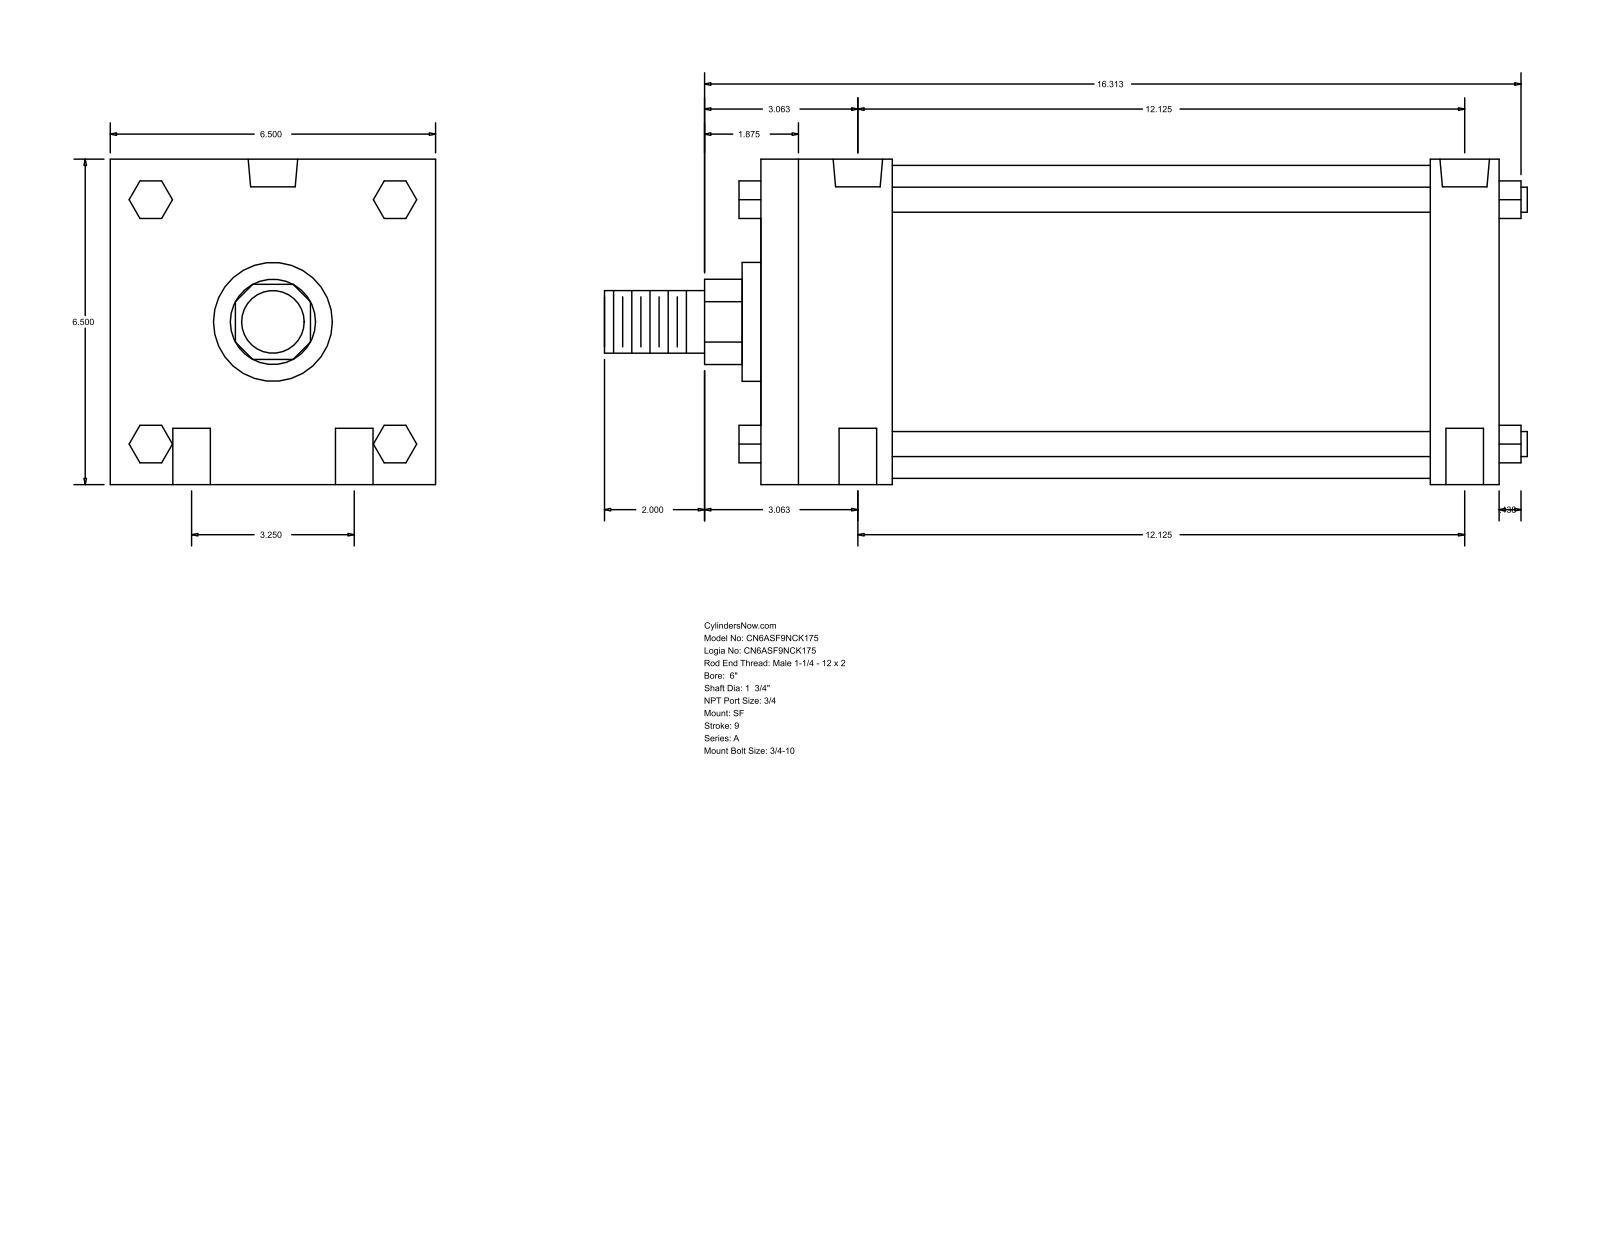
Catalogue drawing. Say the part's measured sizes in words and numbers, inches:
The part is named "A_SF__0600_1.75". Its 3-D file was written by "GSSL Pune (CONFIG_CONTROL_DESIGN)". It is 0 solids with 124 faces: 94 planar, 30 cylindrical and 0 other. Overall it measures 18.437 by 6.5 by 6.5 inches. Round holes: 4 of diameter 0.75, 2 of diameter 0.594, 2 of diameter 0.989. Round bosses or shafts: 4 of diameter 0.5, 1 of diameter 6.25, 1 of diameter 2.375, 1 of diameter 1.75, 1 of diameter 1.25. Partial cylindrical surfaces (rounded edges, fillets, slot ends): 1 of radius 0.852. The main face-to-face distances are 6.5, 14.75, 2.625, 13.375, 1.375, 10.75, 12.125, 0.75, 2.44, 4.226. The hole center spacings are 1.625, 12.233, 12.125, 3.25, 12.553, 11.687.
